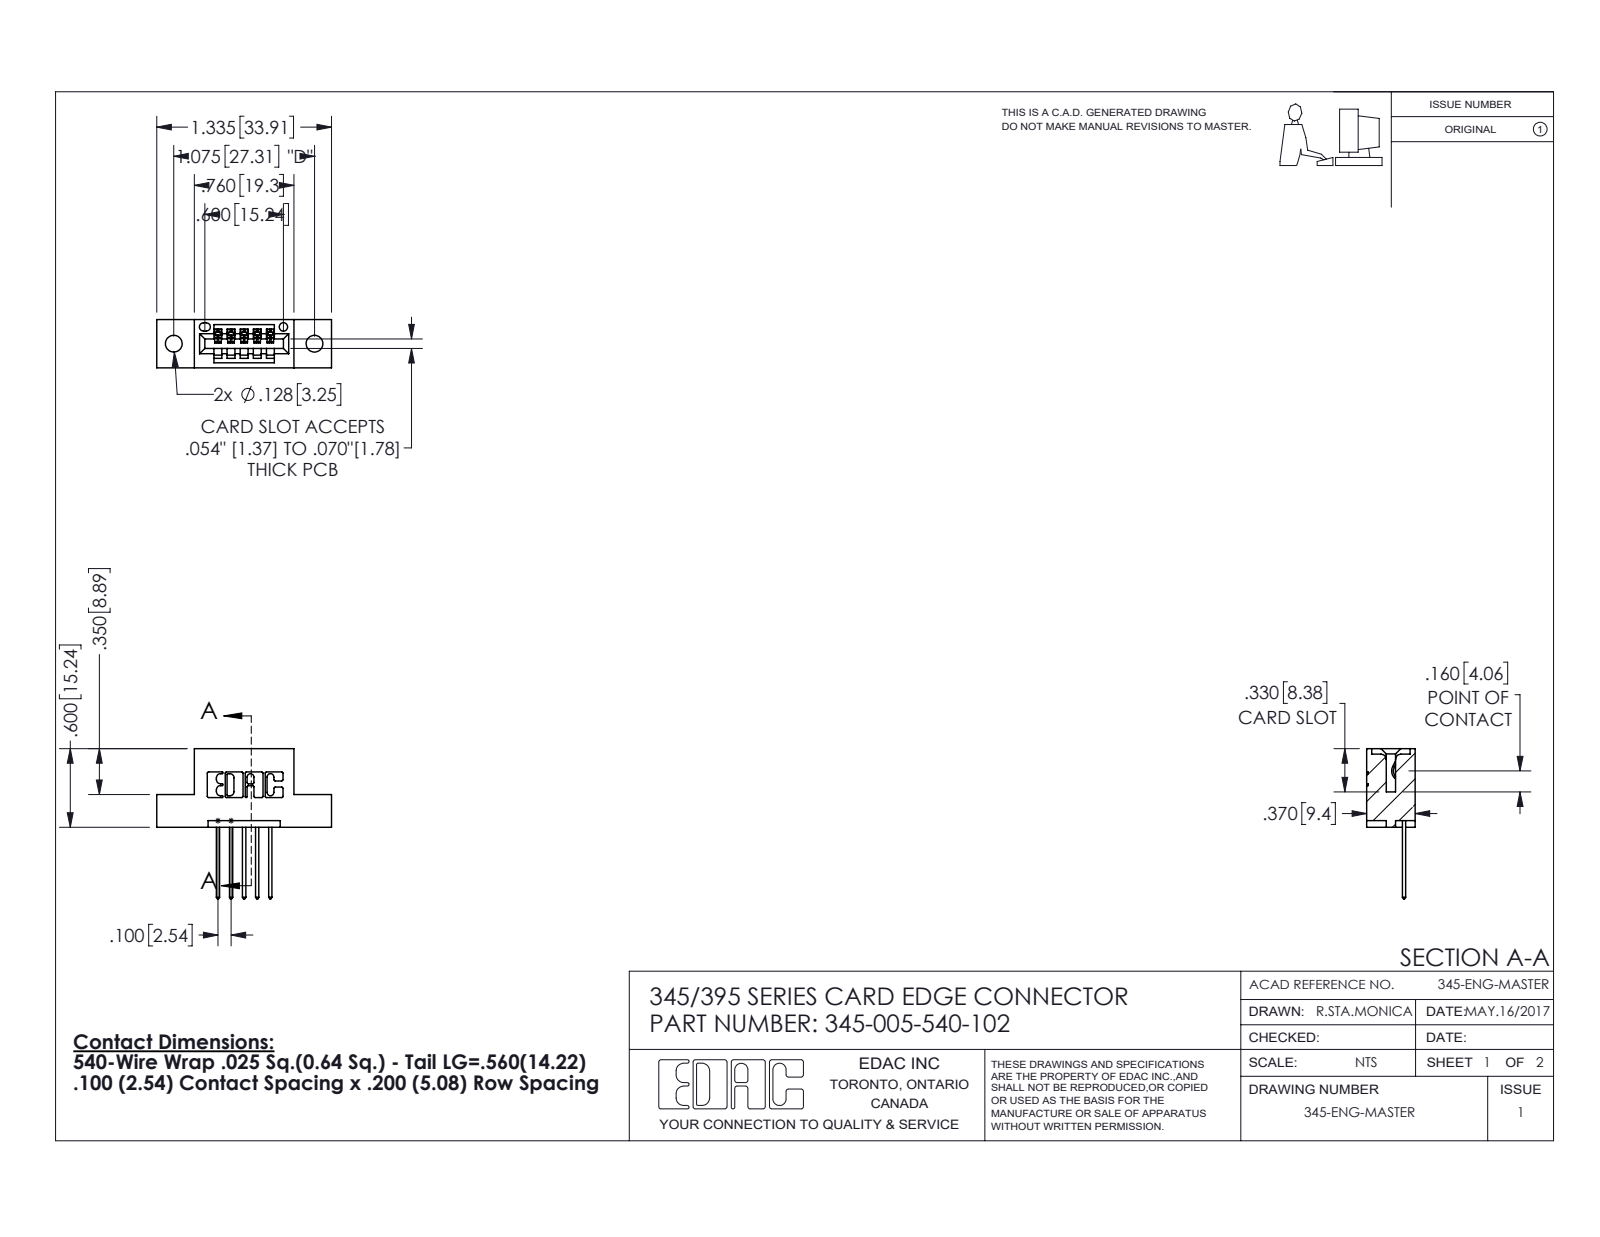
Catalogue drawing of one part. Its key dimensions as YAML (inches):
part_name: "345-005-540-102; 345-292-001_345-293-140; 345 Part_Flush Mounting Lugs - 0.128 Dia"
step_written_by: "SolidWorks 2016 (CONFIG_CONTROL_DESIGN)"
units: inches
bodies: {solids: 6, faces: 416, planar: 280, cylindrical: 136, other: 0}
overall_size: [1.335, 1.147, 0.37]
volume: 0.176
surface_area: 4.823
round_holes:
  - {diameter: 0.128, count: 2}
  - {diameter: 0.064, count: 1}
partial_cylinders:
  - {radius: 0.01, count: 22}
  - {radius: 0.006, count: 10}
  - {radius: 0.01, count: 10}
  - {radius: 0.007, count: 6}
  - {radius: 0.031, count: 6}
  - {radius: 0.026, count: 3}
  - {radius: 0.031, count: 2}
  - {radius: 0.04, count: 2}
face_to_face_distances: [0.2, 0.37, 0.298, 0.072, 0.1, 0.025, 0.098, 0.272, 0.25, 0.06]
hole_center_spacings: [0.27, 0.847, 1.075]
